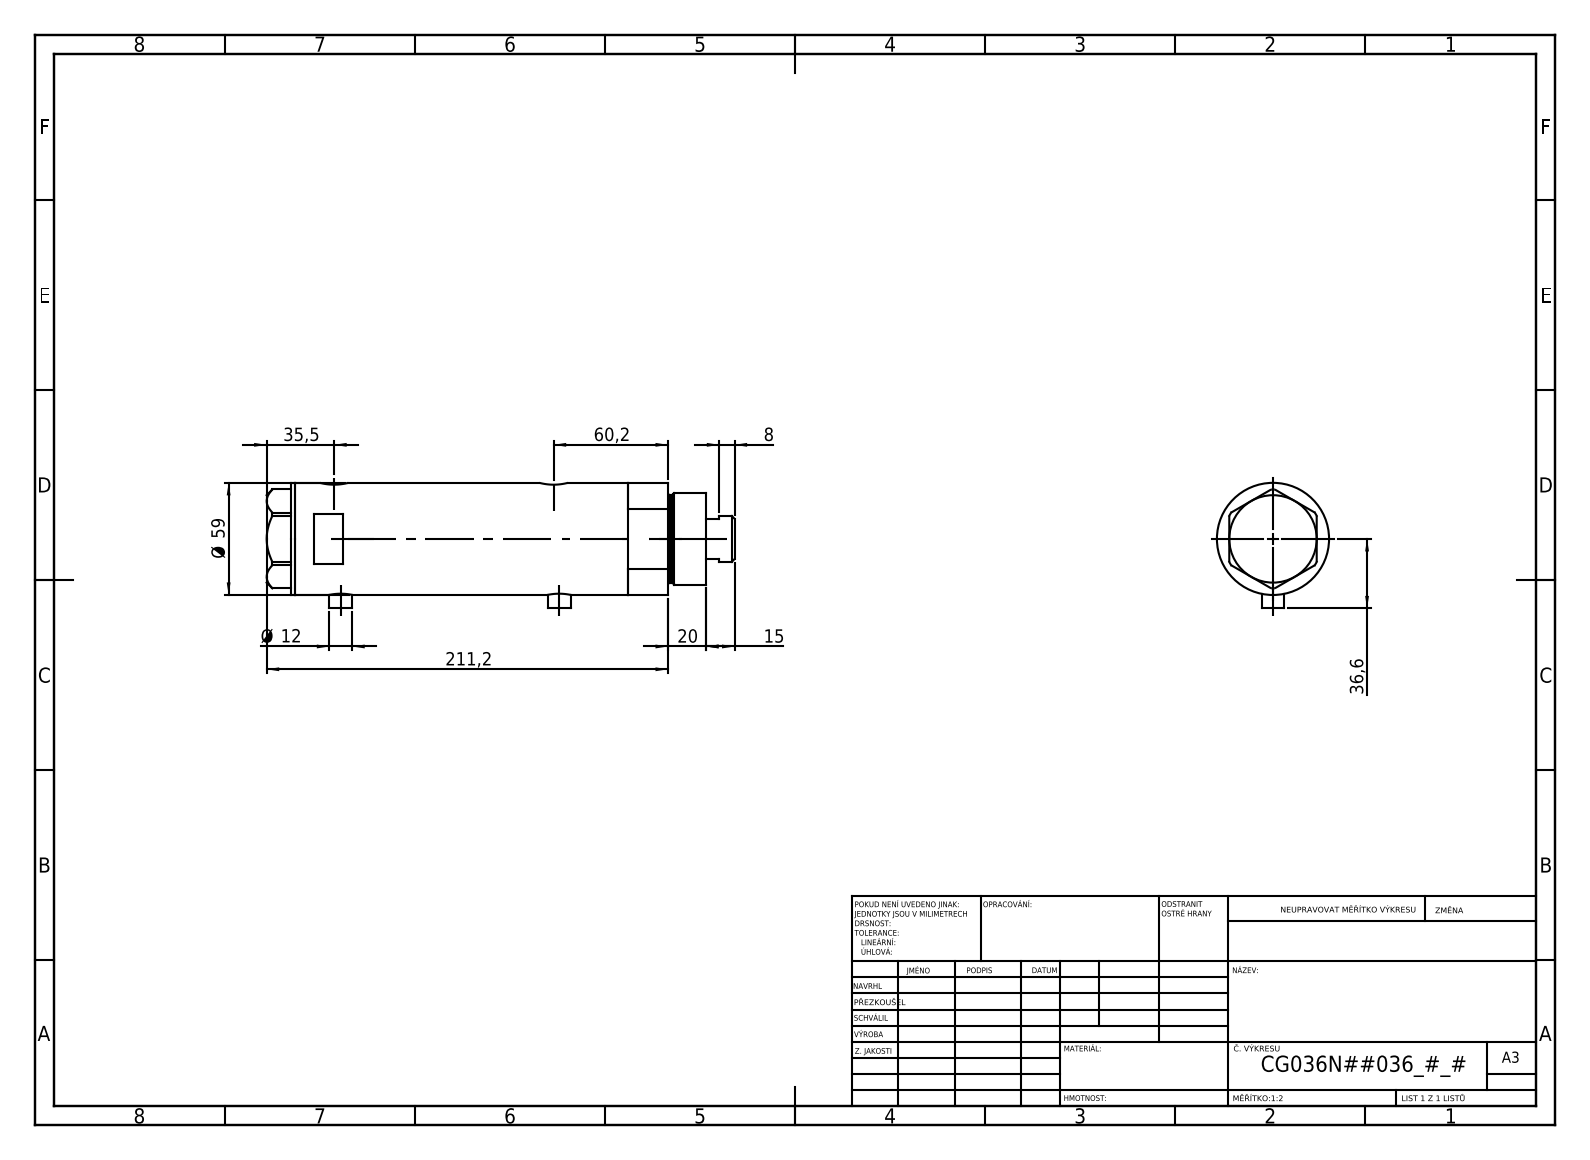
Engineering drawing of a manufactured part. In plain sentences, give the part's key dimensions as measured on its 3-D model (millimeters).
The part is named "V270CG_BACK; V270CG_FRONT; V270CG_VC; V270CG_MIDDLE". Its 3-D file was written by "SolidWorks 2019 (CONFIG_CONTROL_DESIGN)". It is 4 solids with 120 faces: 51 planar, 49 cylindrical and 20 other. Overall it measures 246.2 by 66.1 by 59 millimeters. Its volume is 581 511 cubic millimeters and its surface area 114 863 square millimeters. Round holes: 2 of diameter 9.73, 2 of diameter 12.5, 2 of diameter 15, 1 of diameter 8.5, 1 of diameter 25, 1 of diameter 26.5, 1 of diameter 36, 1 of diameter 40, 1 of diameter 52. Round bosses or shafts: 2 of diameter 12, 1 of diameter 59, 1 of diameter 48, 1 of diameter 46, 1 of diameter 24. The main face-to-face distances are 137.2, 23.5, 113.7, 15, 38.5, 152.2, 2, 231.2, 216.2, 192.7. The hole center spacings are 2.9, 3.5, 112, 114.9, 115.5, 118.4.
